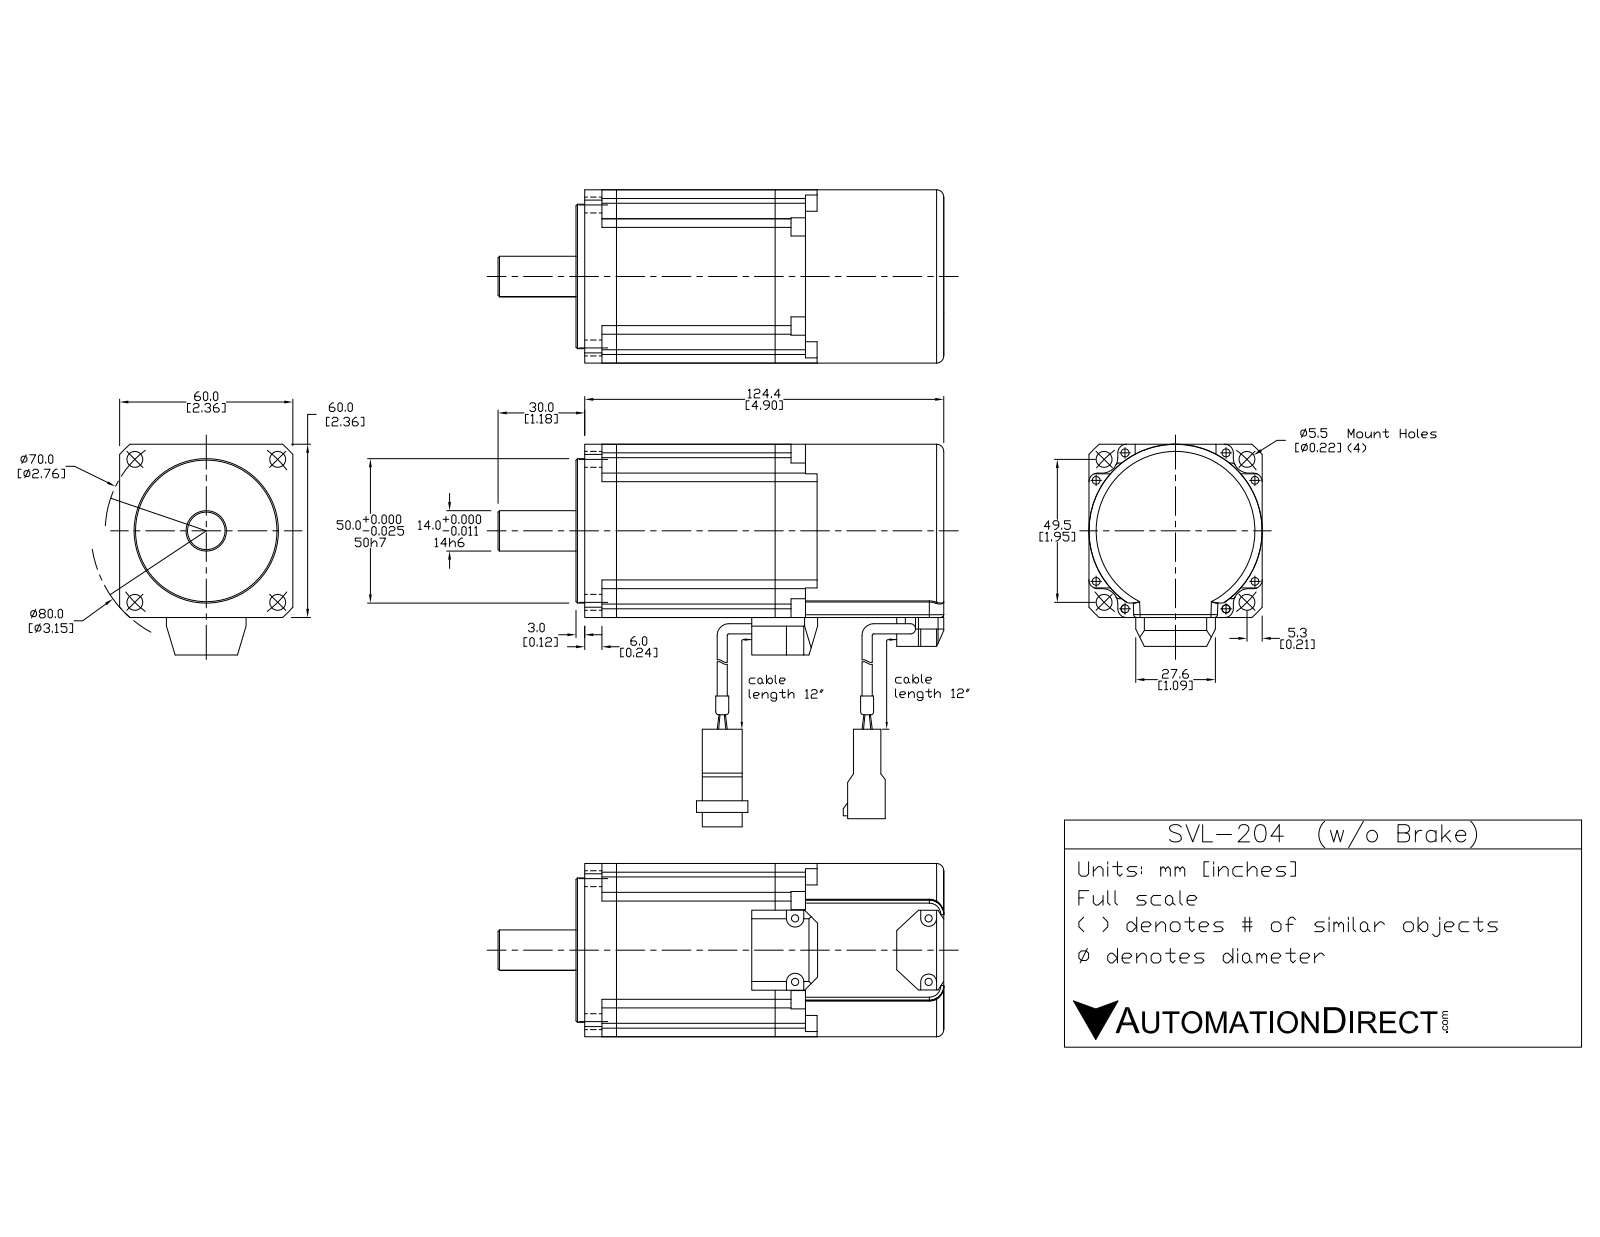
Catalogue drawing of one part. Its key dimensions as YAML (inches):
part_name: "SVL-204"
step_written_by: "SolidWorks 2015 (AUTOMOTIVE_DESIGN)"
units: inches
bodies: {solids: 18, faces: 417, planar: 245, cylindrical: 137, other: 35}
overall_size: [6.079, 2.89, 2.362]
volume: 24.82
surface_area: 93.31
round_holes:
  - {diameter: 0.217, count: 4}
  - {diameter: 0.728, count: 1}
round_bosses_or_shafts:
  - {diameter: 0.217, count: 5}
  - {diameter: 0.197, count: 4}
  - {diameter: 0.138, count: 4}
  - {diameter: 2.362, count: 1}
  - {diameter: 1.969, count: 1}
  - {diameter: 0.551, count: 1}
  - {diameter: 0.276, count: 1}
partial_cylinders:
  - {radius: 0.039, count: 14}
  - {radius: 0.118, count: 12}
  - {radius: 0.079, count: 4}
  - {radius: 0.098, count: 4}
  - {radius: 0.108, count: 4}
  - {radius: 0.209, count: 4}
face_to_face_distances: [2.165, 0.413, 2.579, 2.362, 1.886, 2.299, 4.465, 5.016, 3.13, 2.717]
hole_center_spacings: [1.378, 1.949, 2.756]
